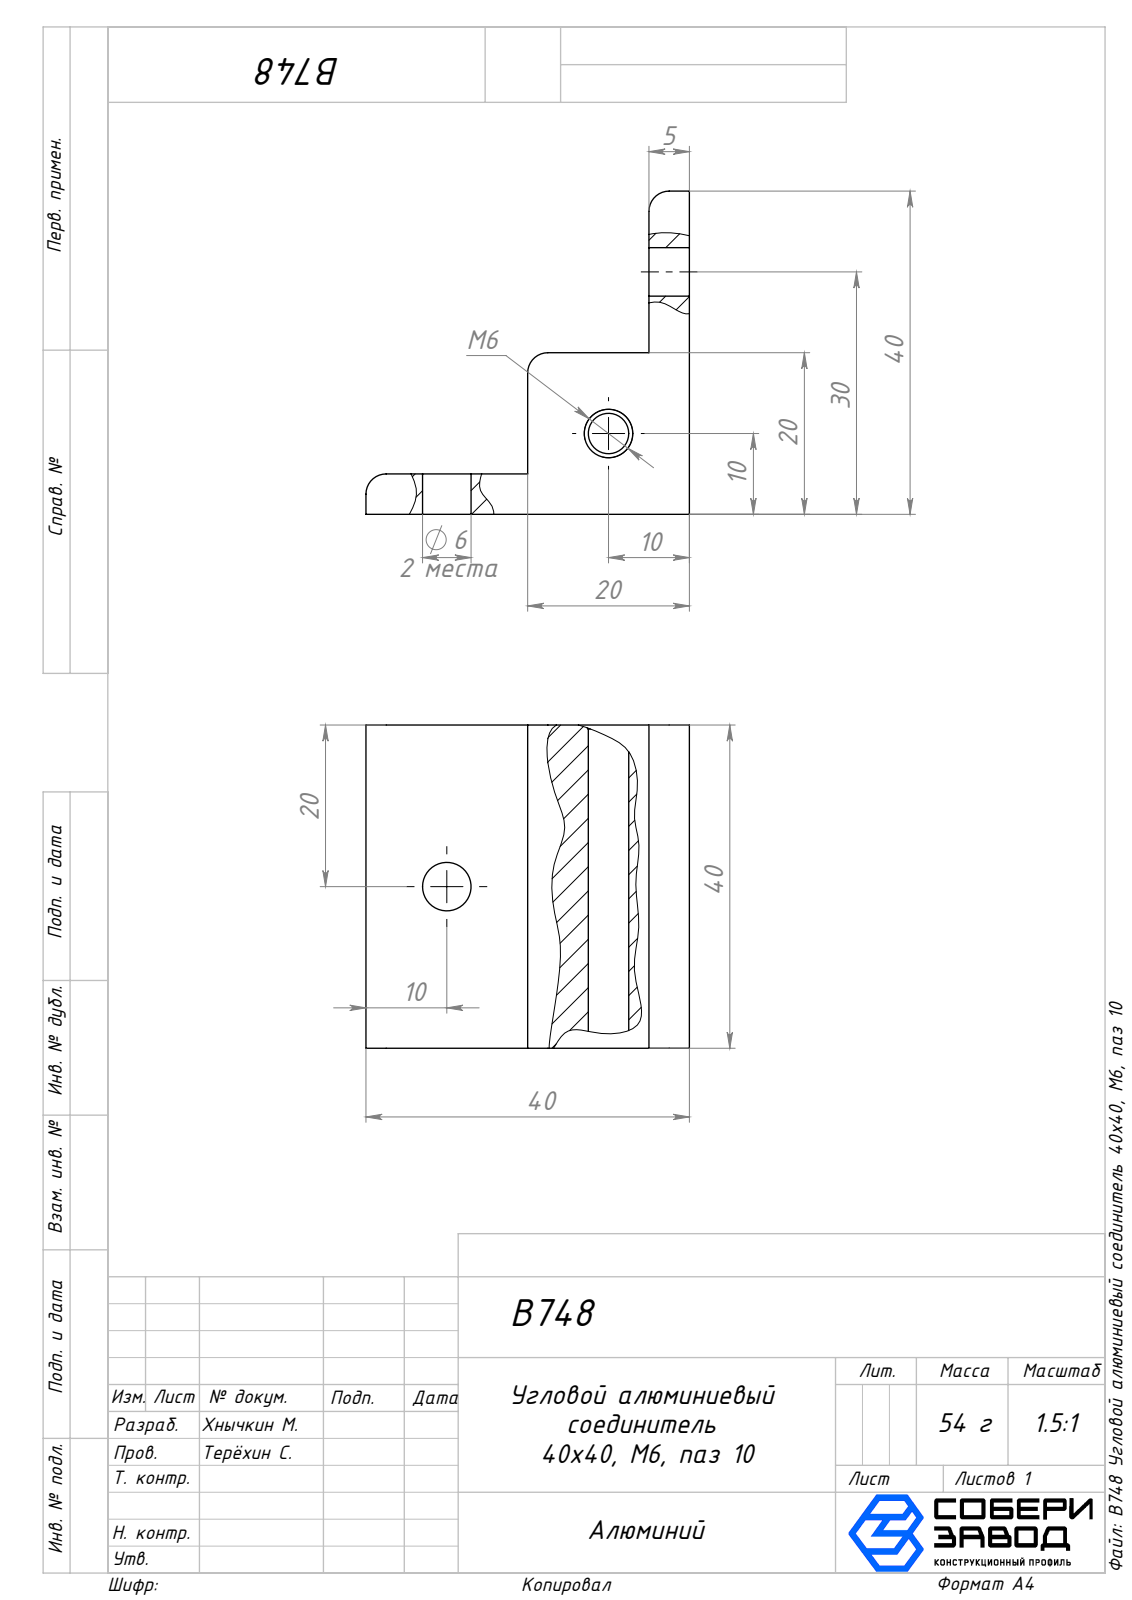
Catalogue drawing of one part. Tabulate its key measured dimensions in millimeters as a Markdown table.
| quantity | value |
| --- | --- |
| part name | B748 Угловой алюминиевый соединитель 40х40, M6, паз 10 |
| STEP written by | SolidWorks 2025 (AUTOMOTIVE_DESIGN) |
| units | millimeters |
| bodies | 1 solid, 23 faces (10 planar, 9 cylindrical, 4 other) |
| overall size | 40 × 40 × 40 |
| volume | 22 767 mm³ |
| surface area | 8 119 mm² |
| round holes (diameter × count) | 6 × 2, 5 × 1 |
| partial cylindrical surfaces (radius × count) | 2.5 × 3 |
| main face-to-face distances | 5, 20, 15, 40, 35 |
